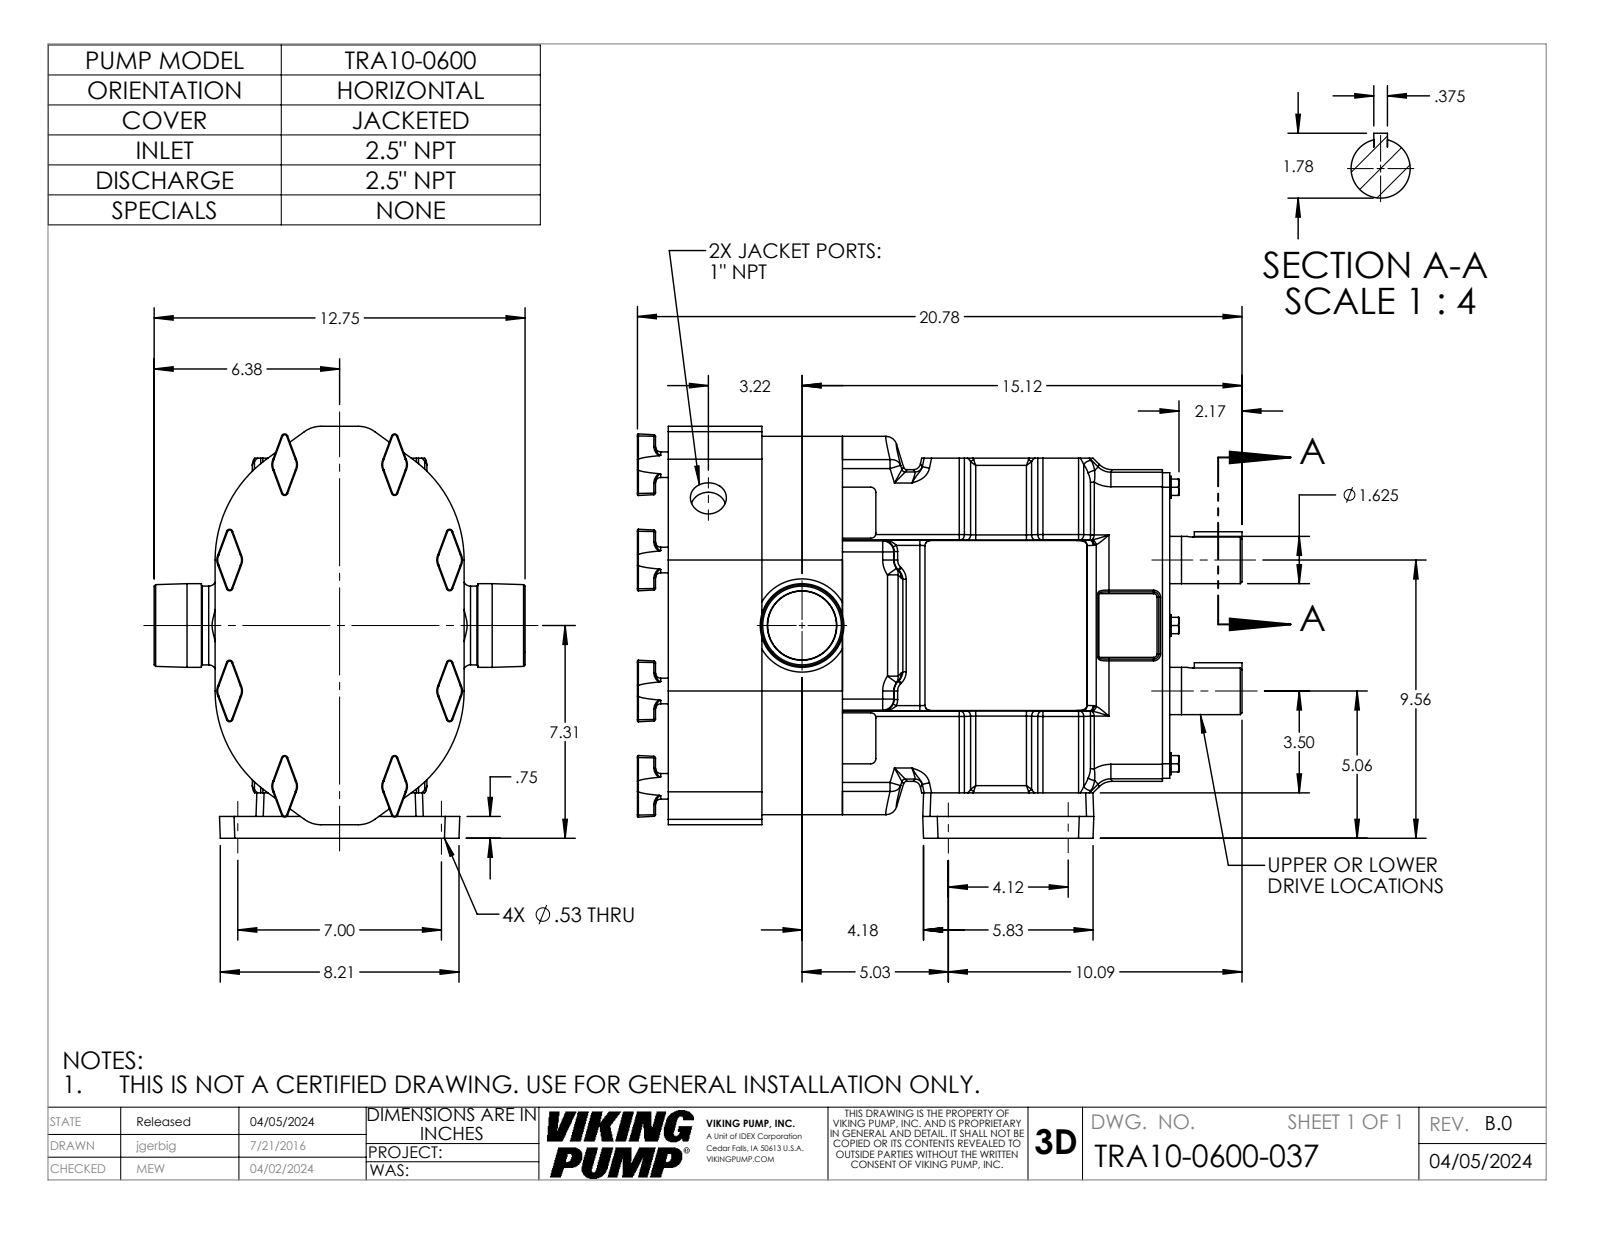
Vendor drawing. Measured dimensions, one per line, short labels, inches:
name: 0600NPT25; TRA10-0600-COVER-JACKET; TRA10-0600-BODY; TRA10-0600-037 (+1 more)
written by: SolidWorks 2022 (AUTOMOTIVE_DESIGN)
unit: in
bodies: 5 solids, 1034 faces (284 planar, 362 cylindrical, 388 other)
size: 20.781 × 14.155 × 12.75
volume: 1 390 in³; area: 1 438 in²
holes: 4× ⌀0.531, 1× ⌀2.368
bosses: 8× ⌀0.88, 6× ⌀0.75, 2× ⌀1.624, 1× ⌀2.875, 1× ⌀2.708
rounds: 44× R0.18, 43× R0.06, 32× R0.03, 30× R0.25, 28× R0.38, 24× R0.12, 20× R0.5, 12× R0.375
face distances: 2.769, 3.218, 5.987, 0.5, 0.36, 17.237, 14.019, 11.25, 6.5, 0.86
hole spacings: 4.12, 7, 8.122
